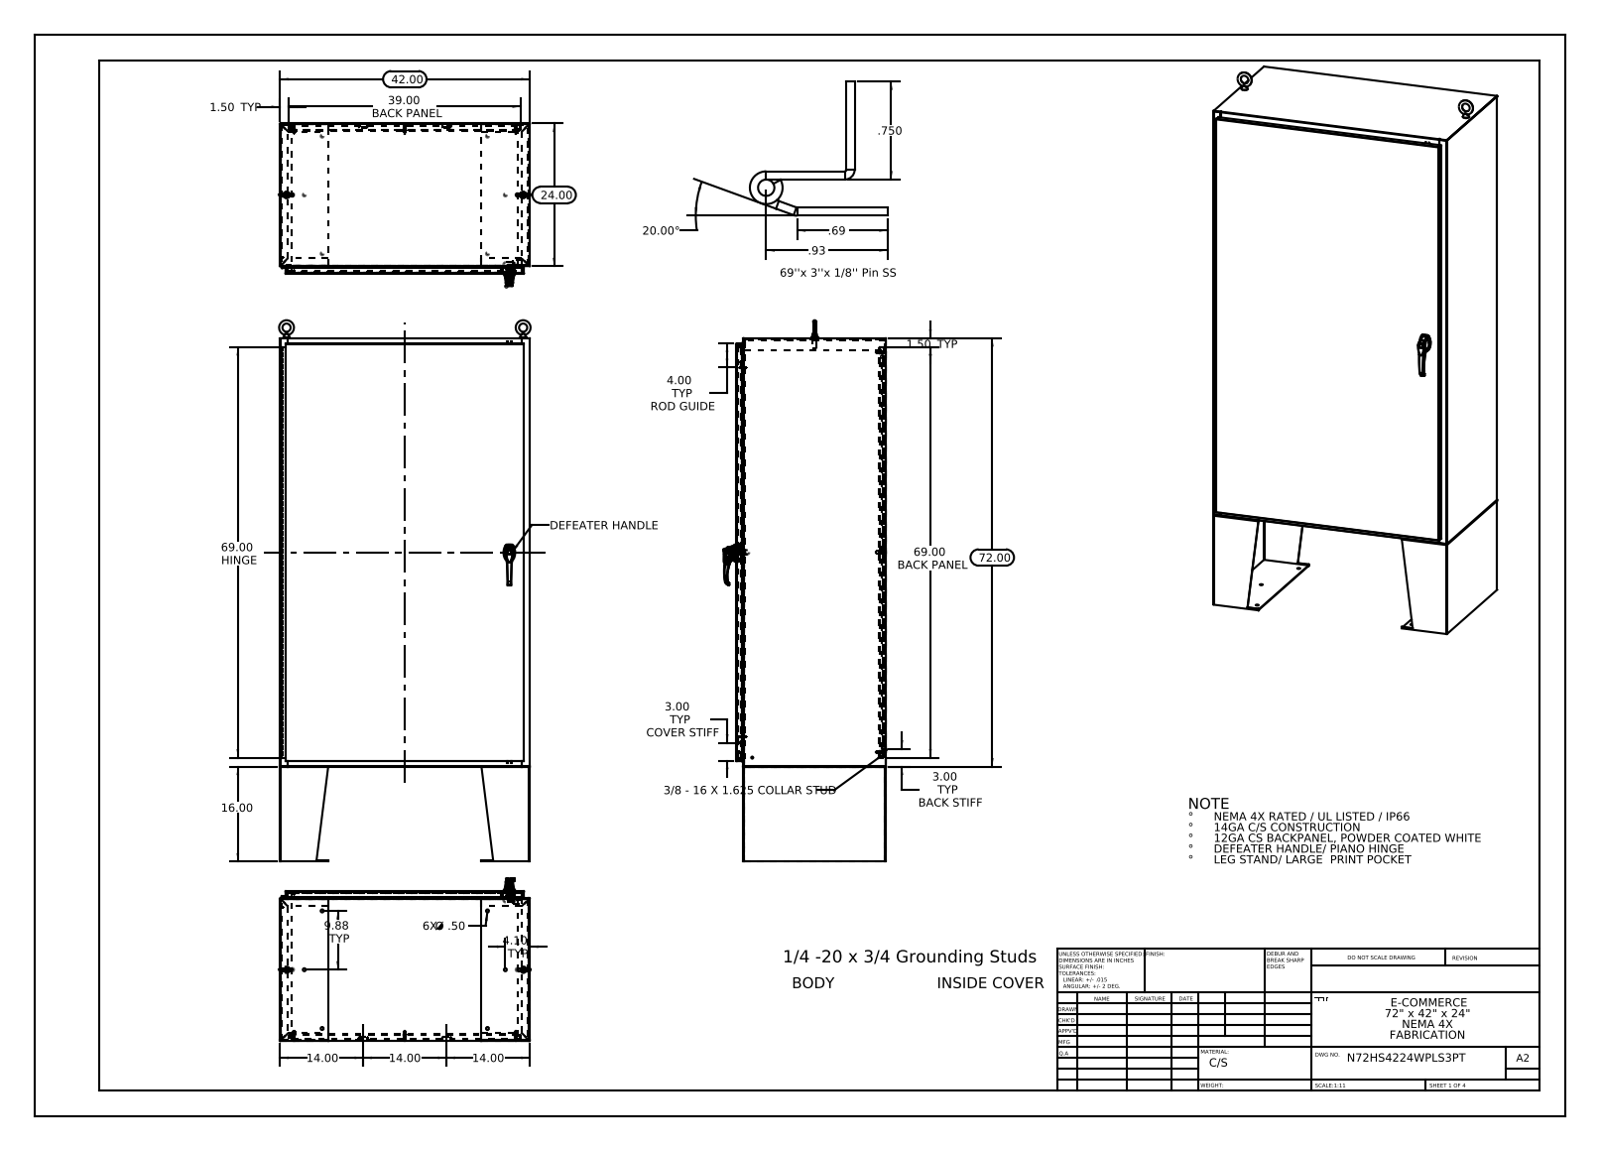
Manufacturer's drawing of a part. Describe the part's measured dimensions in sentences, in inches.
The part is named "N72HS4224SSWPLS3PT Body; NMP-SS-RODGUIDES; N72HS4224SSWPLS3PT 263033_Industrilas; 26161102 (+8 more)". Its 3-D file was written by "SolidWorks 2013 (CONFIG_CONTROL_DESIGN)". It is 55 solids with 4096 faces: 1673 planar, 1605 cylindrical and 818 other. Overall it measures 91 by 42.271 by 27.307 inches. Its volume is 1 468 cubic inches and its surface area 35 541 square inches. Round holes: 14 of diameter 0.5, 10 of diameter 0.25, 4 of diameter 0.75, 3 of diameter 0.138, 3 of diameter 0.161, 2 of diameter 0.079, 2 of diameter 0.203, 2 of diameter 0.313, 2 of diameter 0.437, 1 of diameter 0.125, 1 of diameter 0.125, 1 of diameter 0.197. Round bosses or shafts: 10 of diameter 0.625, 10 of diameter 0.157, 10 of diameter 0.14, 8 of diameter 0.375, 8 of diameter 0.33, 3 of diameter 0.315, 3 of diameter 0.236, 1 of diameter 1.181. Partial cylindrical surfaces (rounded edges, fillets, slot ends): 37 of radius 0.118, 34 of radius 0.013, 33 of radius 0.006, 28 of radius 0.088, 15 of radius 0.039, 12 of radius 0.028, 8 of radius 0.039, 8 of radius 0.143. The main face-to-face distances are 0.075, 25.126, 0.104, 41.925, 25.051, 1.075, 25.201, 1, 24.051, 24.126. The hole center spacings are 10.324, 11.553, 16.578, 29.353, 31.661, 33.625, 35.196, 38.439.
